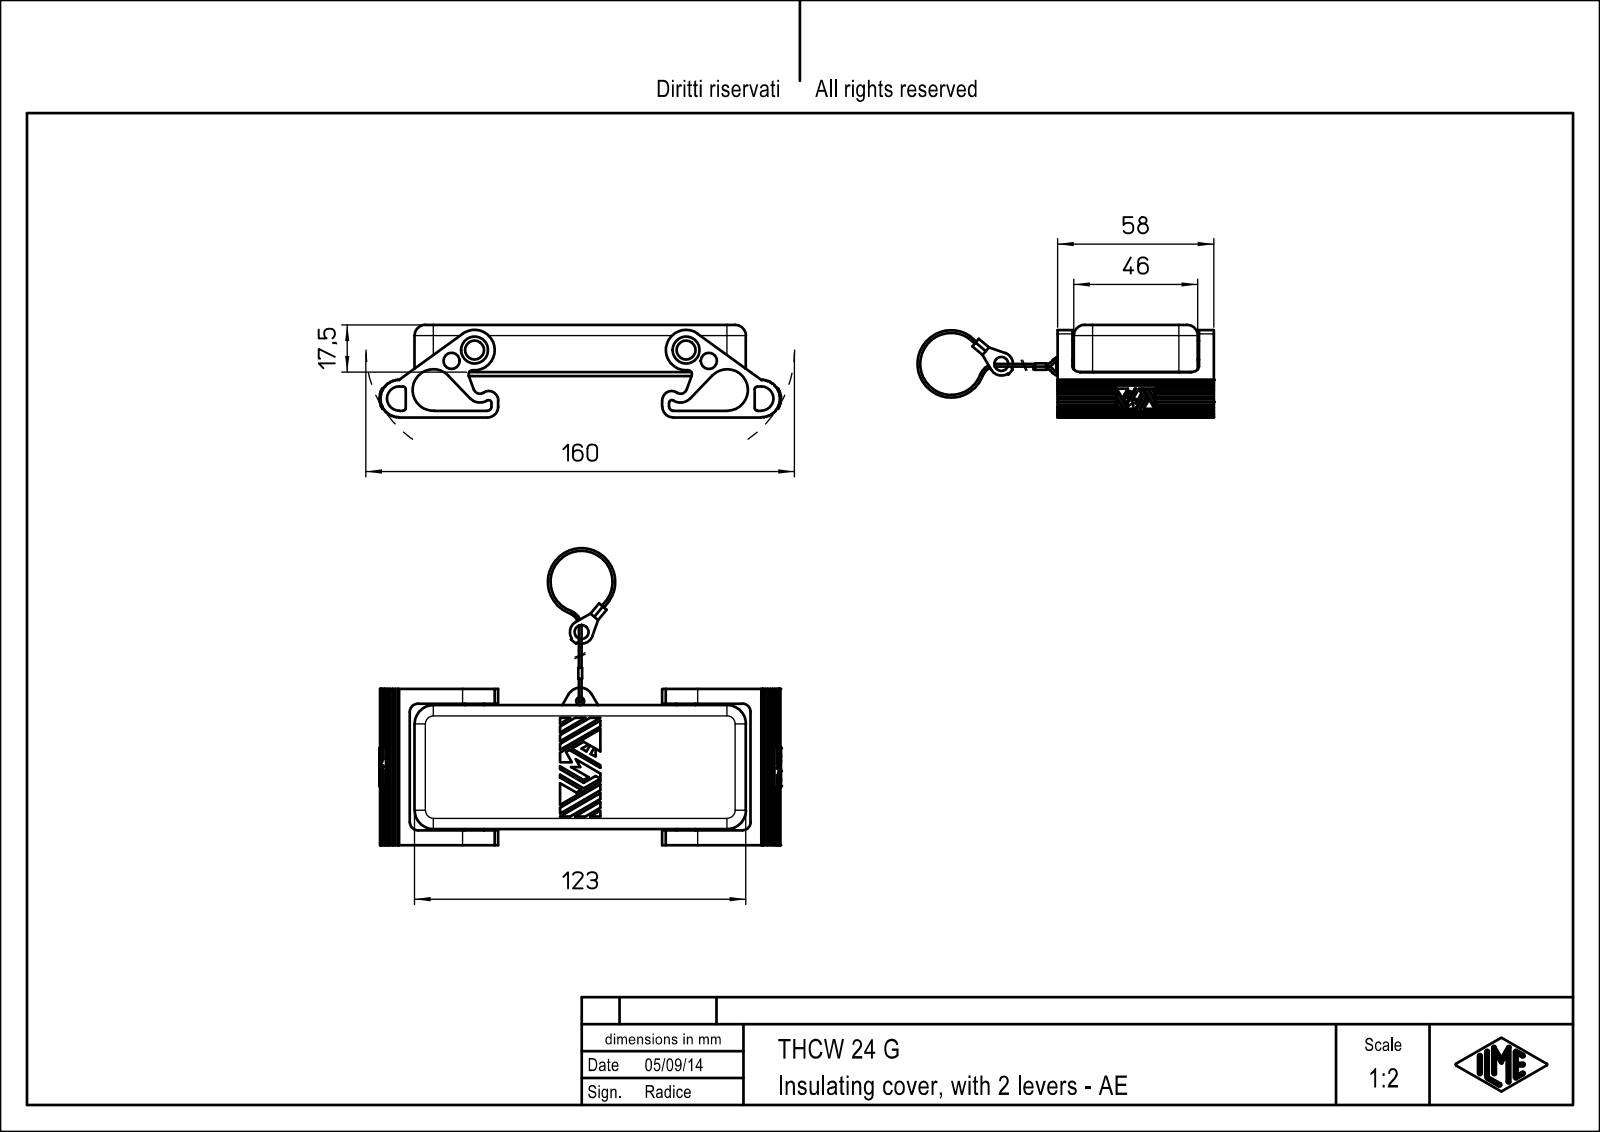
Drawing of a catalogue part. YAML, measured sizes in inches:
part_name: "THCW 24 G"
step_written_by: "Creo Elements/Direct Modeling 20.1B 02-Apr-2019 (C) Parametric Technology GmbH (AUTOMOTIVE_DESIGN)"
units: inches
bodies: {solids: 1, faces: 604, planar: 214, cylindrical: 302, other: 88}
overall_size: [8.971, 5.925, 1.36]
volume: 4.651
surface_area: 61.93
round_holes:
  - {diameter: 0.118, count: 1}
  - {diameter: 0.165, count: 1}
round_bosses_or_shafts:
  - {diameter: 0.039, count: 5}
  - {diameter: 0.276, count: 3}
partial_cylinders:
  - {radius: 0.006, count: 44}
  - {radius: 0.039, count: 40}
  - {radius: 0.059, count: 18}
  - {radius: 0.051, count: 16}
  - {radius: 0.118, count: 16}
  - {radius: 0.02, count: 12}
  - {radius: 0.079, count: 12}
  - {radius: 0.157, count: 10}
face_to_face_distances: [0.217, 2.067, 1.85, 0.472, 0.689, 1.354, 1.138, 0.665, 2.283, 4.98]
